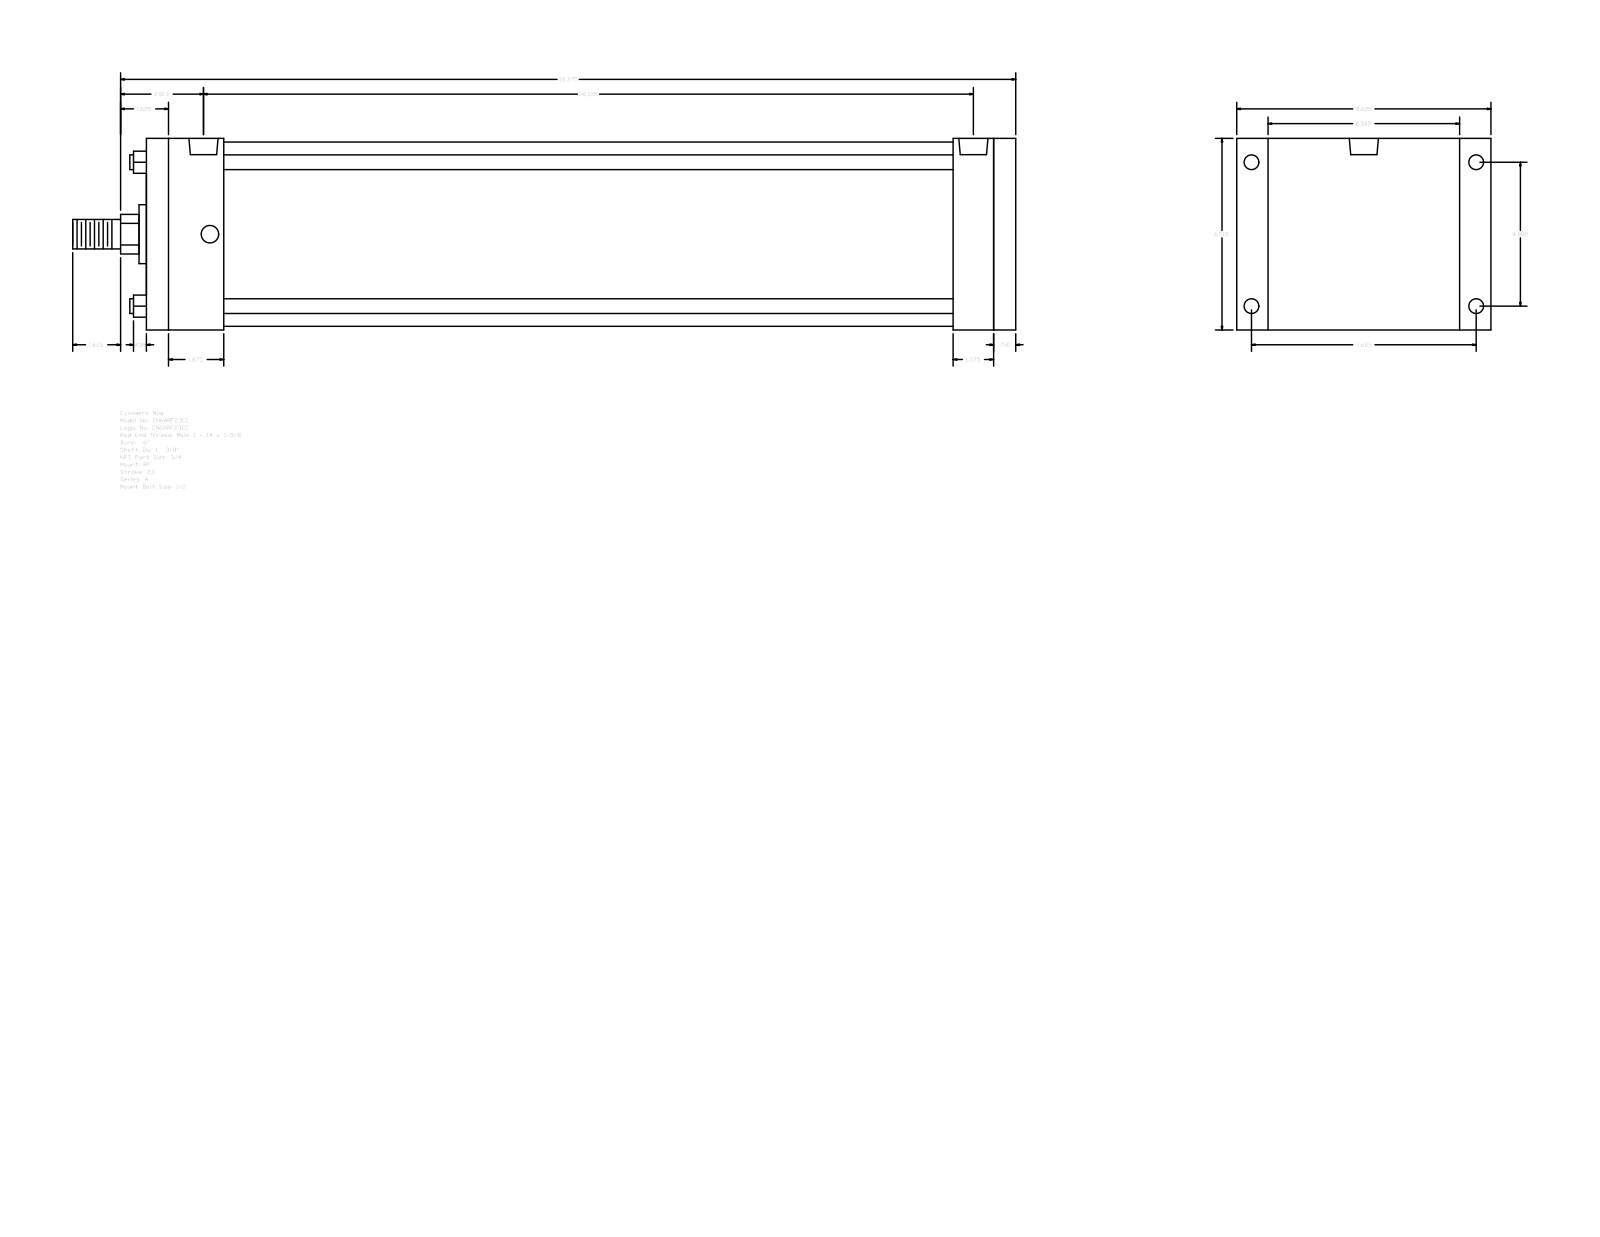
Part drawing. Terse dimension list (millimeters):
name: A_RF__0600_1.375
written by: GSSL Pune (CONFIG_CONTROL_DESIGN)
unit: mm
bodies: 0 solids, 92 faces (64 planar, 28 cylindrical, 0 other)
size: 812.8 × 219.07 × 165.1
holes: 4× ⌀12.7, 4× ⌀15.08, 2× ⌀25.12
bosses: 4× ⌀12.7, 1× ⌀158.75, 1× ⌀50.8, 1× ⌀34.92, 1× ⌀25.4
rounds: 1× R17.06
face distances: 165.1, 749.29, 730.25, 19.04, 53.97, 66.67, 663.58, 682.62, 695.32, 628.65
hole spacings: 5.56, 123.96, 193.68, 229.95, 652.45, 658.01, 663.57
